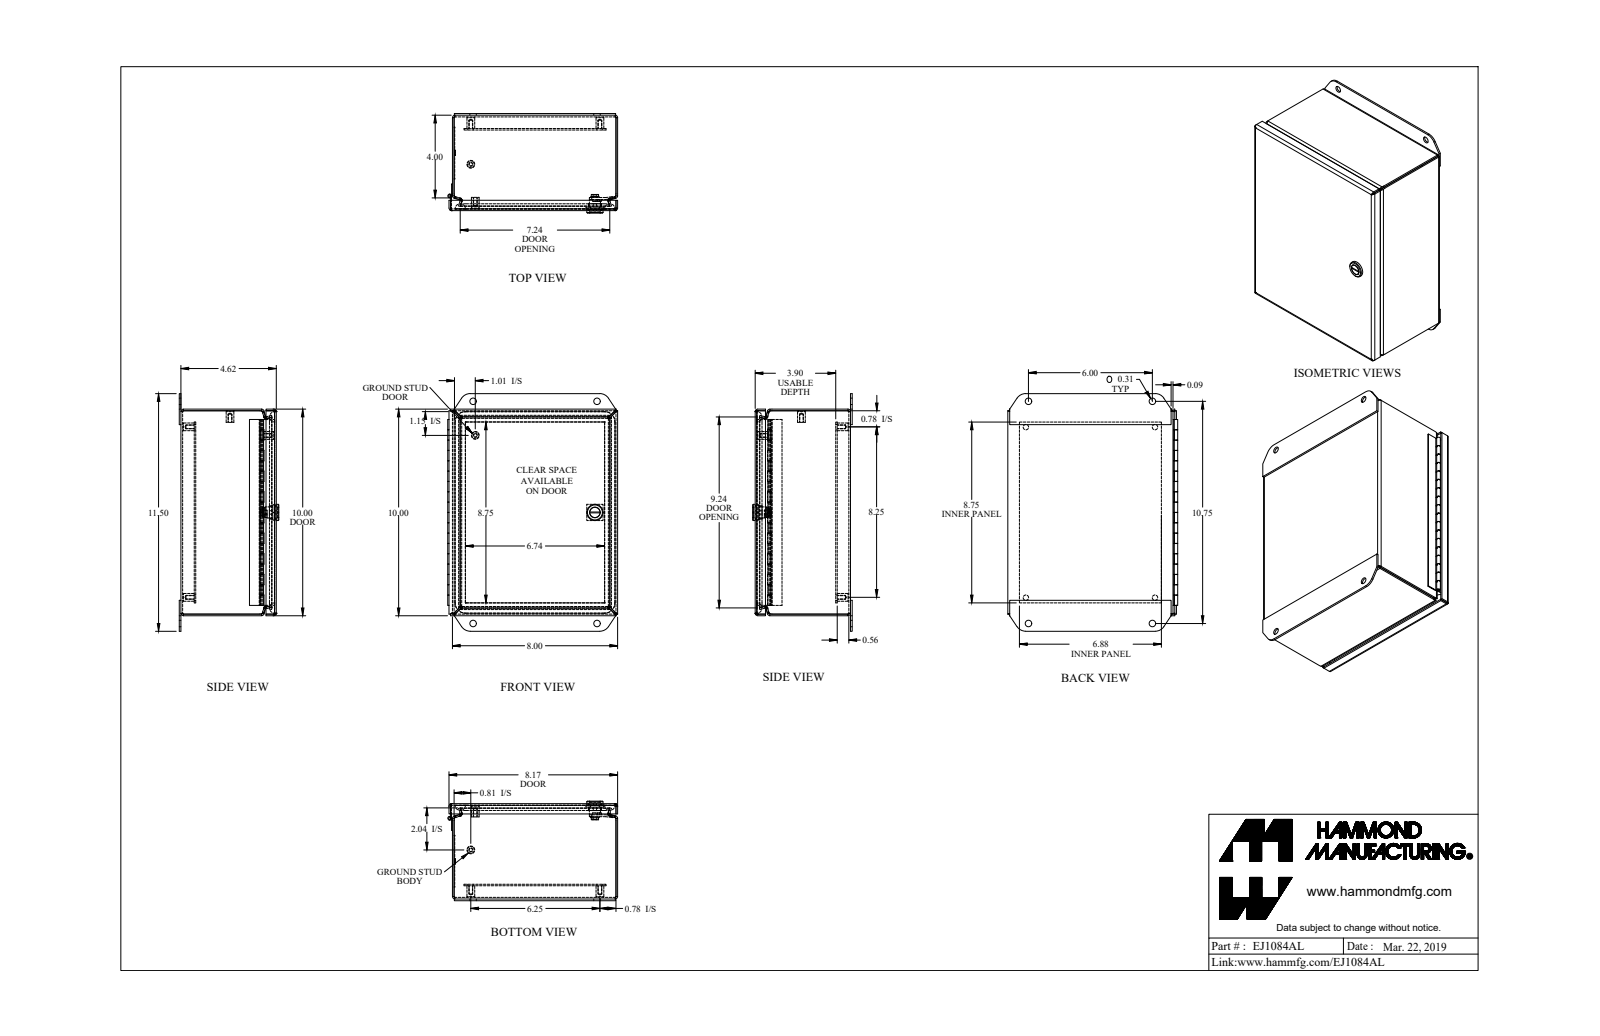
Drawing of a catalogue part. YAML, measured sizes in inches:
part_name: "EJ1084AL_Default"
step_written_by: "SolidWorks 2019 (CONFIG_CONTROL_DESIGN)"
units: inches
bodies: {solids: 14, faces: 622, planar: 398, cylindrical: 156, other: 68}
overall_size: [11.5, 8.226, 4.82]
volume: 37.54
surface_area: 960.1
round_holes:
  - {diameter: 0.159, count: 6}
  - {diameter: 0.265, count: 4}
  - {diameter: 0.313, count: 4}
  - {diameter: 0.516, count: 1}
round_bosses_or_shafts:
  - {diameter: 0.375, count: 6}
  - {diameter: 0.33, count: 6}
  - {diameter: 0.788, count: 1}
  - {diameter: 0.535, count: 1}
  - {diameter: 0.496, count: 1}
  - {diameter: 0.435, count: 1}
  - {diameter: 0.18, count: 1}
  - {diameter: 0.1, count: 1}
partial_cylinders:
  - {radius: 0.041, count: 16}
  - {radius: 0.121, count: 16}
  - {radius: 0.281, count: 12}
  - {radius: 0.25, count: 4}
  - {radius: 0.499, count: 4}
  - {radius: 0.5, count: 4}
  - {radius: 0.06, count: 2}
  - {radius: 0.03, count: 1}
face_to_face_distances: [0.081, 4.536, 4.617, 7.919, 4.455, 9.919, 0.643, 0.562, 3.974, 3.893]
hole_center_spacings: [1.257, 6.252, 9.501, 10.35, 11.304, 0.024, 4.131, 5.376]
